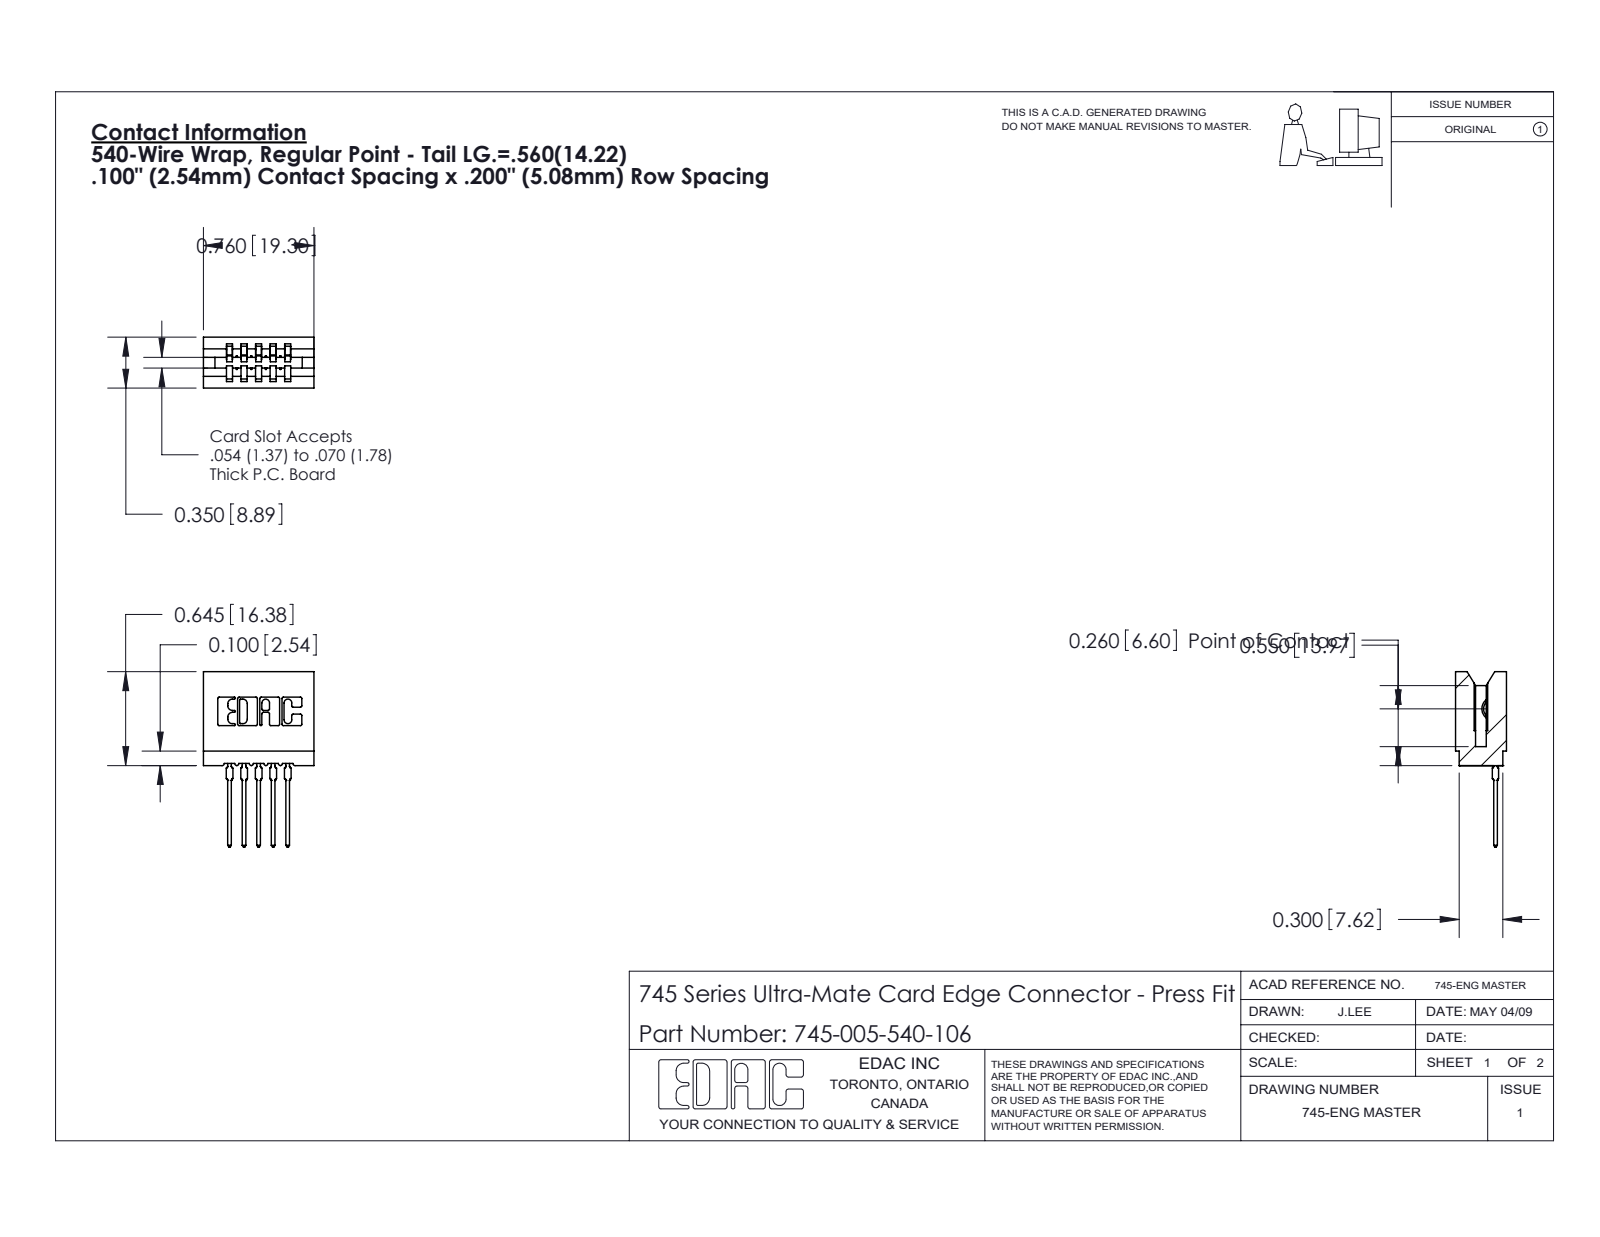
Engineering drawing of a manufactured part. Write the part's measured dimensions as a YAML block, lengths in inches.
part_name: "745-005-540-106; 745 Part_Insulator Option - 06; 745-292-001_540"
step_written_by: "SolidWorks 2020 (CONFIG_CONTROL_DESIGN)"
units: inches
bodies: {solids: 6, faces: 656, planar: 391, cylindrical: 135, other: 130}
overall_size: [1.206, 0.76, 0.35]
volume: 0.116
surface_area: 4.493
partial_cylinders:
  - {radius: 0.01, count: 22}
  - {radius: 0.015, count: 10}
  - {radius: 0.021, count: 10}
  - {radius: 0.007, count: 6}
  - {radius: 0.031, count: 6}
  - {radius: 0.005, count: 4}
  - {radius: 0.011, count: 4}
  - {radius: 0.026, count: 3}
face_to_face_distances: [0.1, 0.2, 0.042, 0.3, 0.142, 0.058, 0.35, 0.158, 0.242, 0.138]
